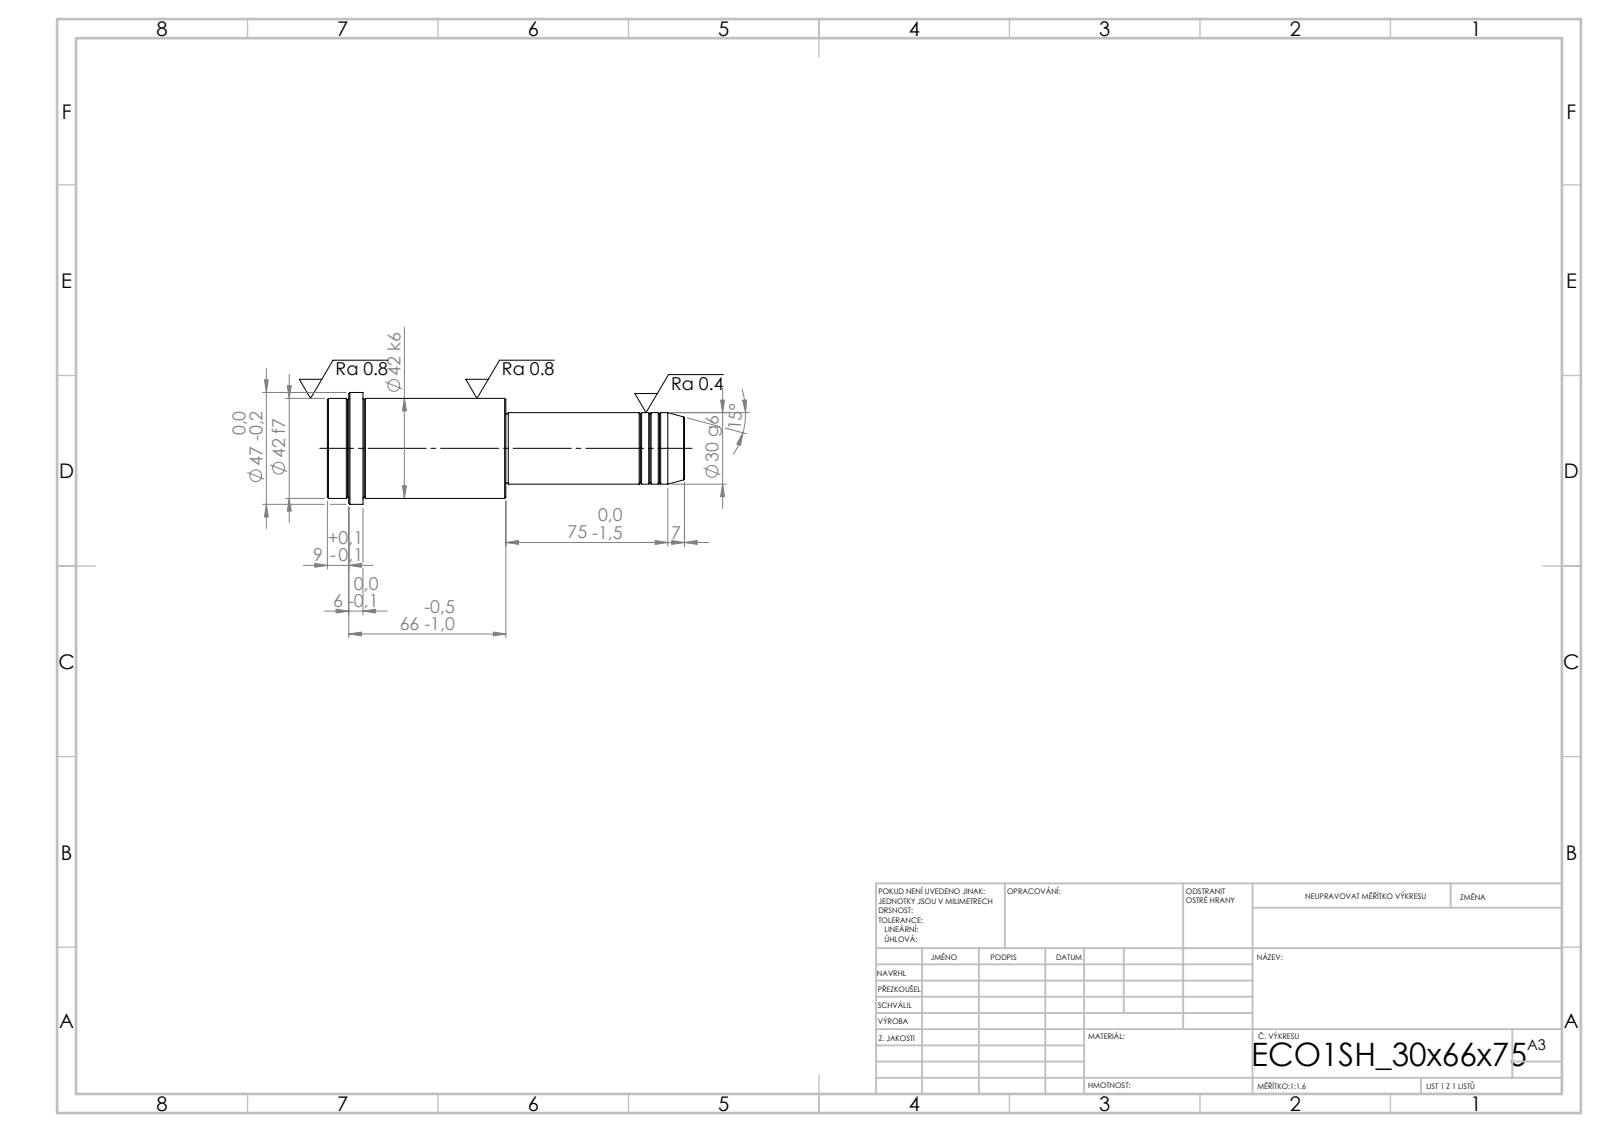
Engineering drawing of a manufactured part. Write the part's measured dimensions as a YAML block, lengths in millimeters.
step_written_by: "SolidWorks 2019 (CONFIG_CONTROL_DESIGN)"
units: millimeters
bodies: {solids: 1, faces: 52, planar: 6, cylindrical: 16, other: 30}
overall_size: [150, 47, 47]
volume: 158115
surface_area: 20599
round_bosses_or_shafts:
  - {diameter: 47, count: 1}
  - {diameter: 42, count: 1}
  - {diameter: 30, count: 1}
  - {diameter: 29, count: 1}
face_to_face_distances: [75, 150, 135, 60, 15, 141, 66, 6, 9, 74]
